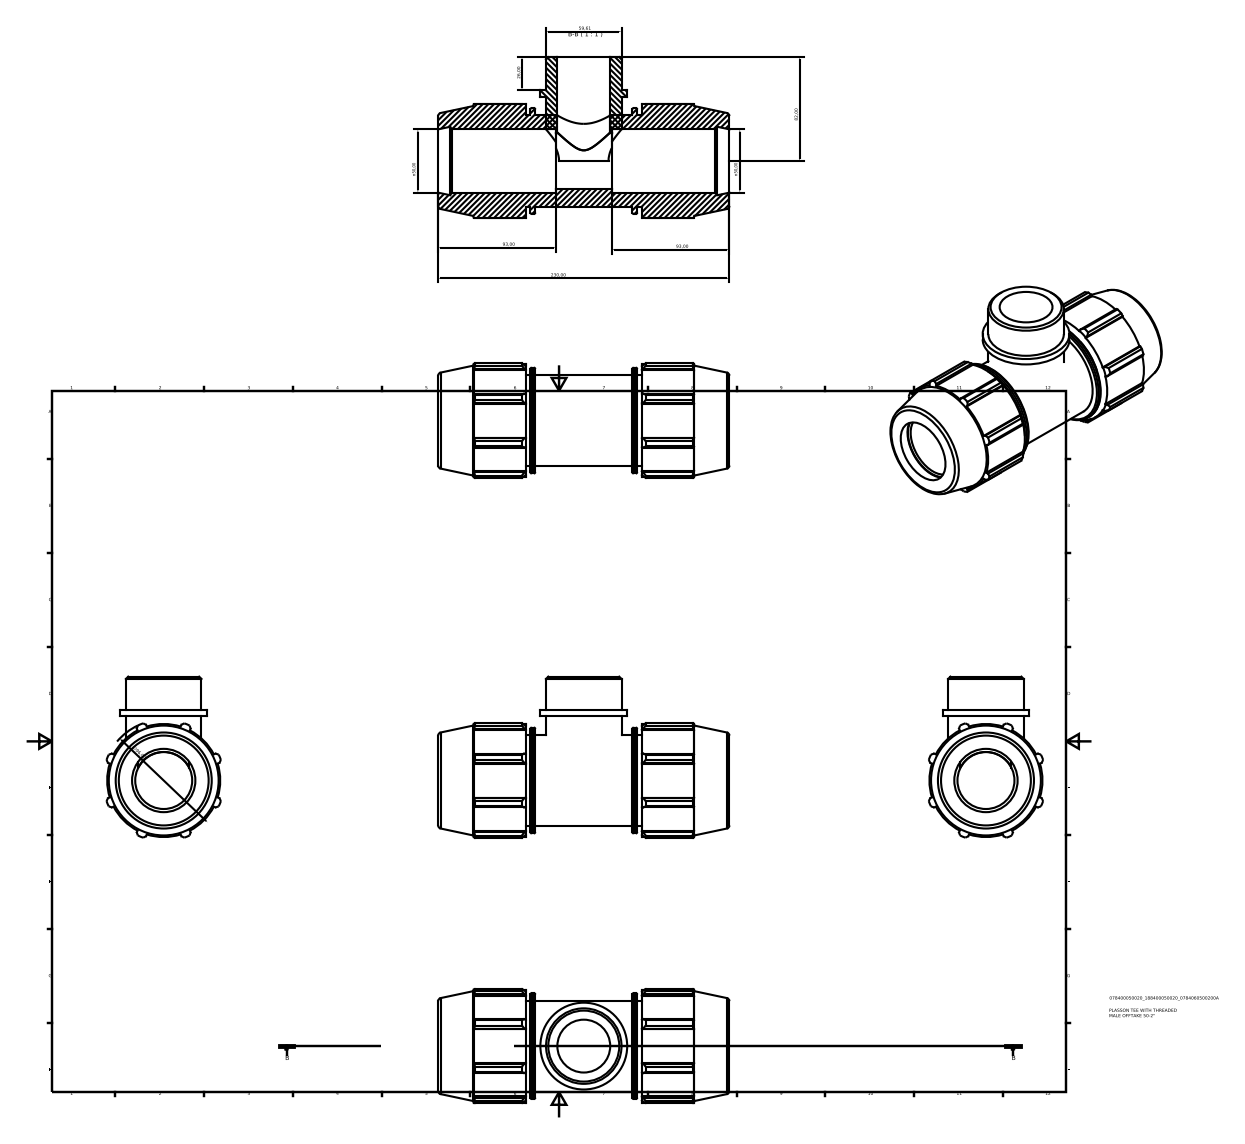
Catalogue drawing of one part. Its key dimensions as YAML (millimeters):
part_name: "078400050020_188400050020"
step_written_by: "Autodesk Inventor 2015 (AUTOMOTIVE_DESIGN)"
units: millimeters
bodies: {solids: 2, faces: 162, planar: 83, cylindrical: 48, other: 31}
overall_size: [230, 127.17, 90.33]
volume: 846071
surface_area: 140497
round_holes:
  - {diameter: 41.73, count: 1}
  - {diameter: 45, count: 1}
  - {diameter: 50, count: 1}
round_bosses_or_shafts:
  - {diameter: 83.52, count: 1}
  - {diameter: 72, count: 1}
  - {diameter: 68.56, count: 1}
  - {diameter: 59.61, count: 1}
partial_cylinders:
  - {radius: 44.64, count: 1}
  - {radius: 48, count: 1}
face_to_face_distances: [69, 161, 72.83, 157.17, 3.83, 88.17, 76.67, 153.33, 7.67, 84.33]
